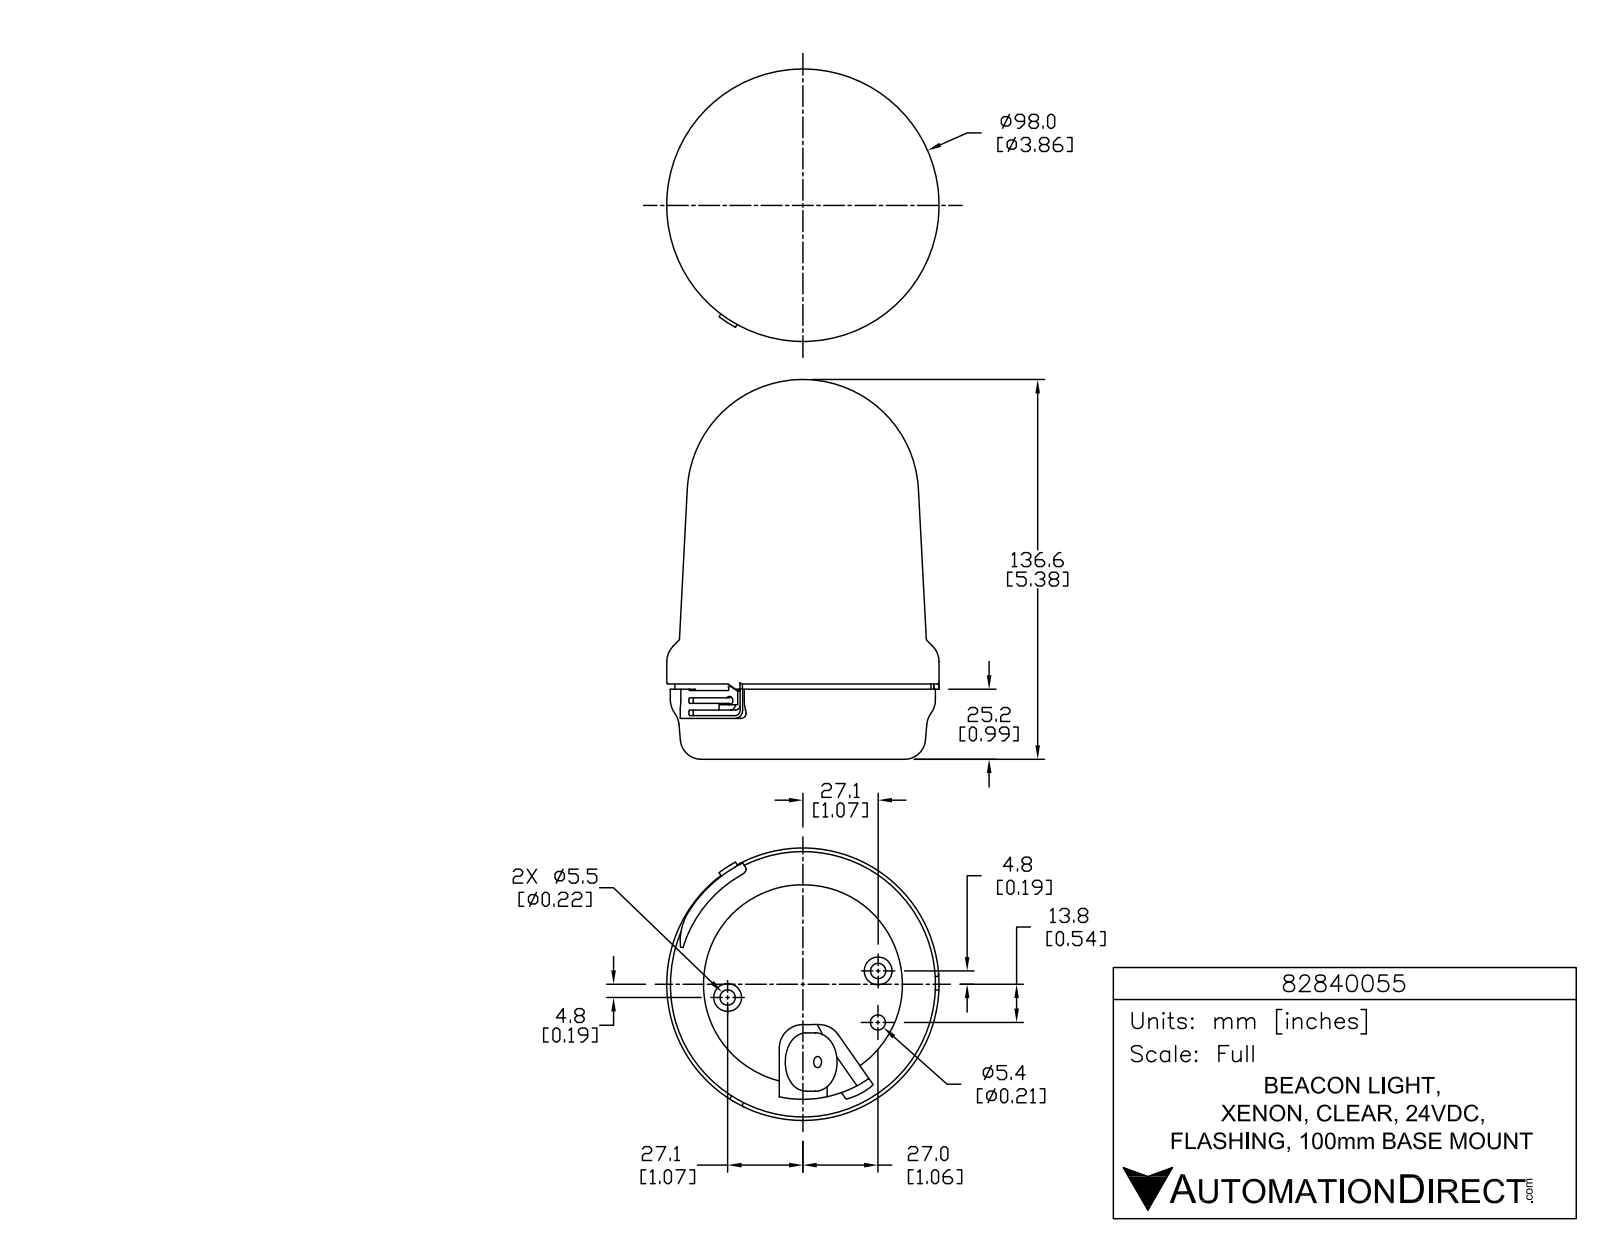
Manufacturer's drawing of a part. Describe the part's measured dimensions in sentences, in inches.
The part is named "82840055". Its 3-D file was written by "SolidWorks 2015 (AUTOMOTIVE_DESIGN)". It is 1 solid with 872 faces: 566 planar, 204 cylindrical and 102 other. Overall it measures 5.378 by 3.858 by 3.858 inches. Its volume is 44.69 cubic inches and its surface area 73.66 square inches. Round holes: 3 of diameter 0.059, 2 of diameter 0.217, 1 of diameter 0.157, 1 of diameter 0.213, 1 of diameter 2.819. Round bosses or shafts: 3 of diameter 0.339, 3 of diameter 0.084, 2 of diameter 0.394, 1 of diameter 3.858, 1 of diameter 3.756, 1 of diameter 3.626, 1 of diameter 0.827. Partial cylindrical surfaces (rounded edges, fillets, slot ends): 9 of radius 0.005, 6 of radius 0.005, 6 of radius 0.012, 6 of radius 0.012, 6 of radius 0.012, 6 of radius 0.196, 5 of radius 0.02, 4 of radius 0.039. The main face-to-face distances are 1.045, 0.972, 0.073, 0.02, 0.992, 1.065, 0.236, 0.579, 0.559, 0.413. The hole center spacings are 1.083, 0.73, 1.193, 2.158, 2.165.
